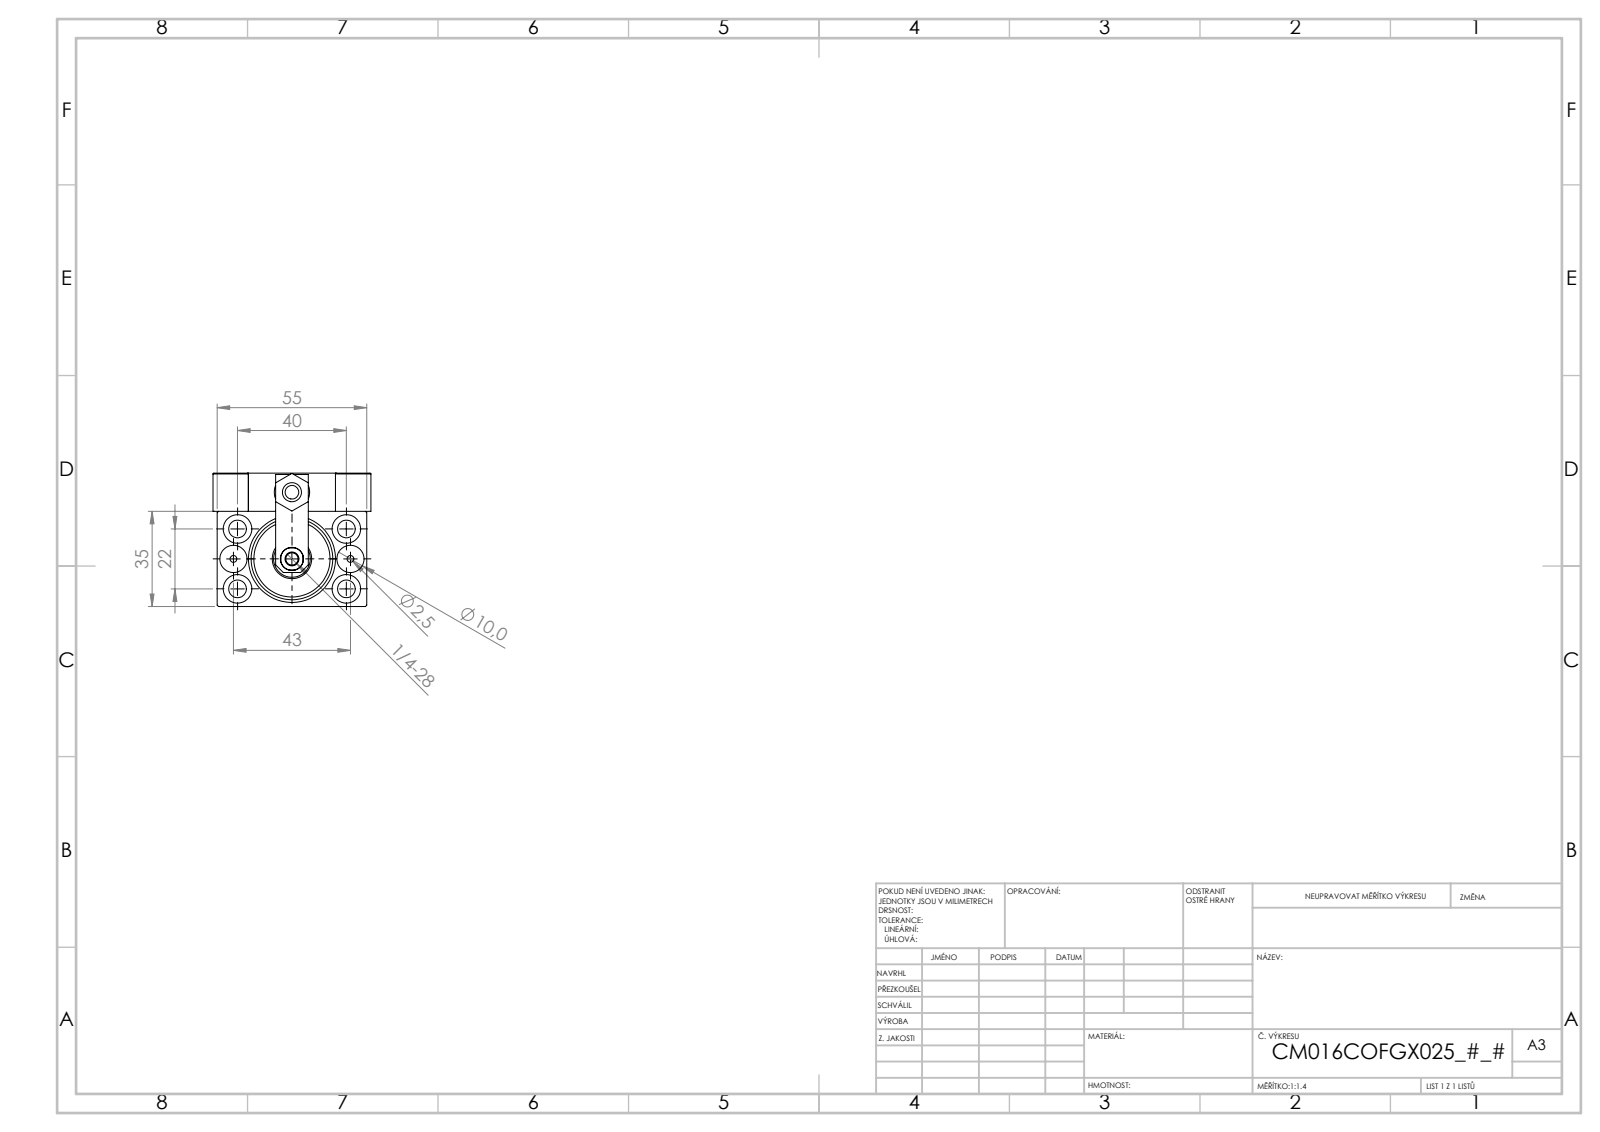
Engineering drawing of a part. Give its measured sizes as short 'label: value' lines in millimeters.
name: SWITCH_X_FRONT_BACK; ZARAZKA; MAGNET; Block (+7 more)
written by: SolidWorks 2019 (CONFIG_CONTROL_DESIGN)
unit: mm
bodies: 23 solids, 1281 faces (561 planar, 186 cylindrical, 534 other)
size: 141.7 × 58 × 49
volume: 163 302 mm³; area: 55 710 mm²
holes: 5× ⌀8, 4× ⌀3.2, 4× ⌀4, 4× ⌀6.5, 4× ⌀10.5, 3× ⌀10, 2× ⌀2.5, 2× ⌀5, 1× ⌀4.5, 1× ⌀7, 1× ⌀8.5, 1× ⌀13.5
bosses: 2× ⌀5, 2× ⌀3.8, 1× ⌀13, 1× ⌀11
rounds: 30× R0.3, 2× R3, 1× R4.5
face distances: 35, 5, 49, 14, 55, 10, 3, 7, 59, 1.5
hole spacings: 11.1, 22.83, 42.93, 11.37, 20, 21.5, 22, 23.09
